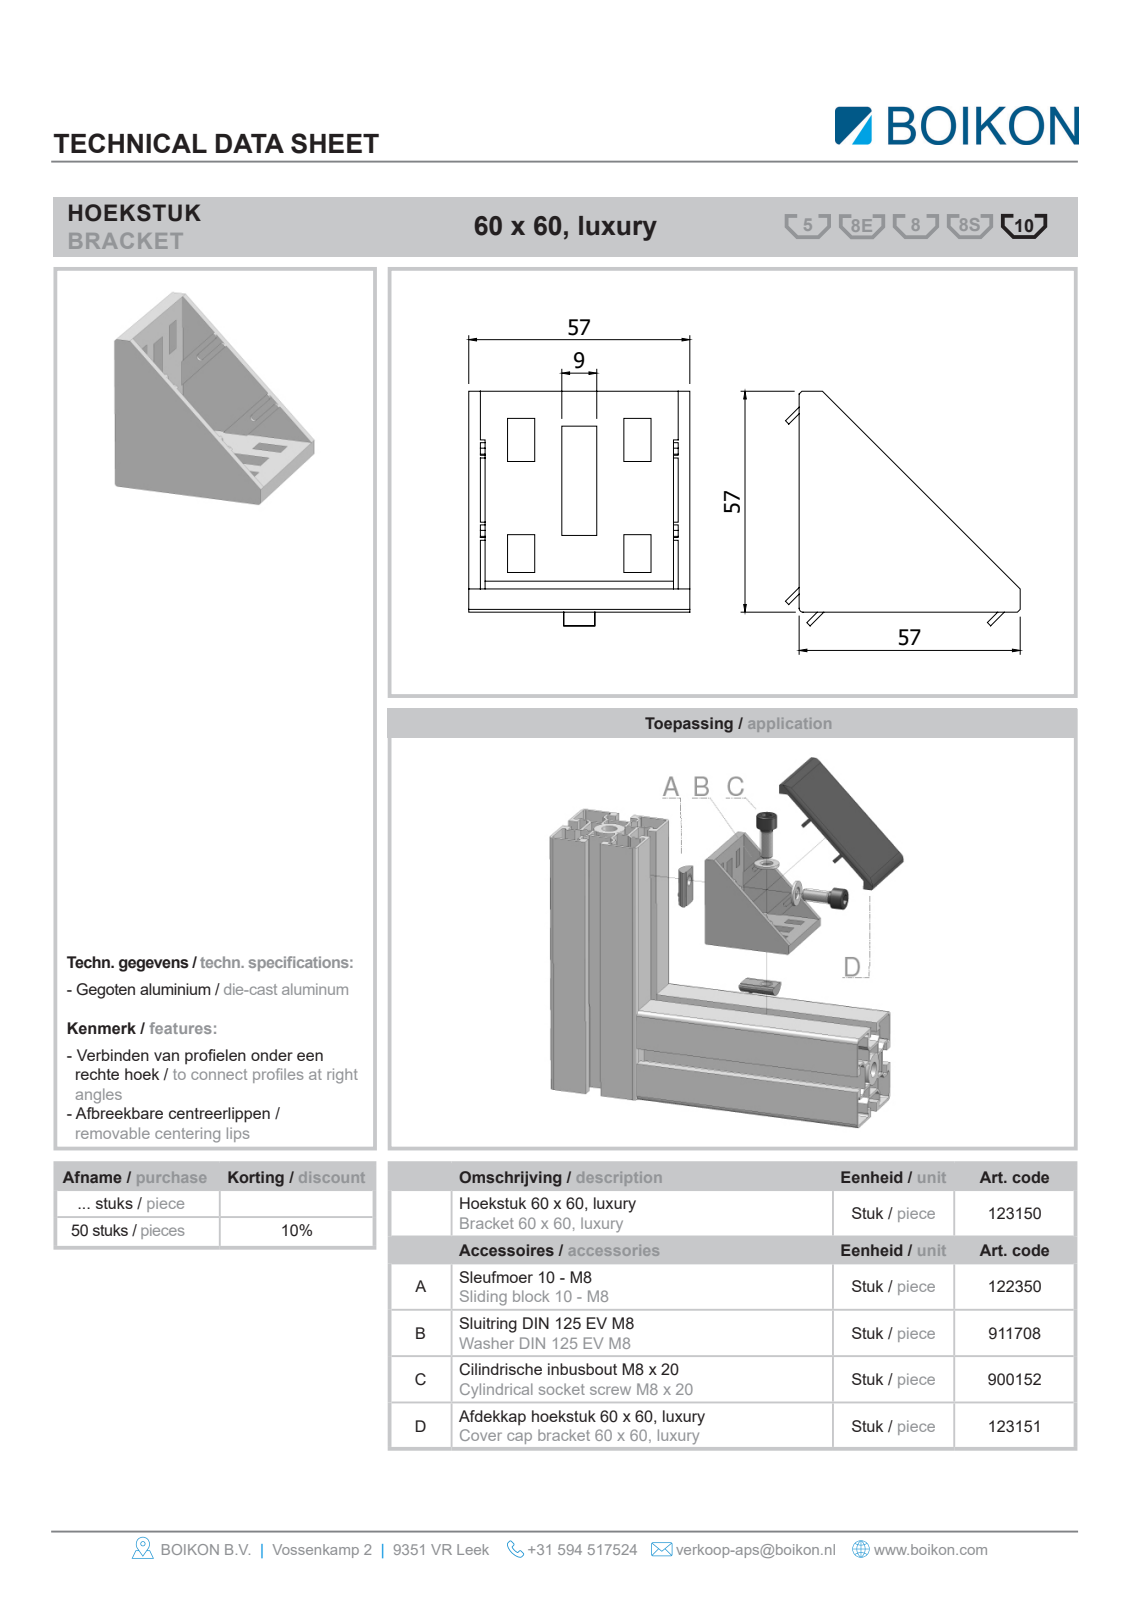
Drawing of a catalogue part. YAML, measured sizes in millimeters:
part_name: "Root; 123150HOEKSTUK 60X60 LUXURYBOIKON; 123151AFDEKKAP HOEKSTUK 60X60BOIKON; 900152Cil. inbusbout DIN 912 EV M8 x 20BOIKON0 (+2 more)"
step_written_by: "HiCAD 2013 1802.4 Build 509 (AUTOMOTIVE_DESIGN)"
units: millimeters
bodies: {solids: 8, faces: 306, planar: 261, cylindrical: 37, other: 8}
overall_size: [76.21, 76.21, 57]
volume: 57286
surface_area: 40345
round_holes:
  - {diameter: 8, count: 2}
  - {diameter: 8.4, count: 2}
round_bosses_or_shafts:
  - {diameter: 16, count: 2}
  - {diameter: 13, count: 2}
  - {diameter: 6.47, count: 2}
partial_cylinders:
  - {radius: 1, count: 5}
  - {radius: 3, count: 4}
  - {radius: 2, count: 3}
  - {radius: 1.3, count: 2}
  - {radius: 7, count: 2}
  - {radius: 8, count: 2}
face_to_face_distances: [3, 6, 54, 57, 30, 7, 51, 14, 47, 37]
